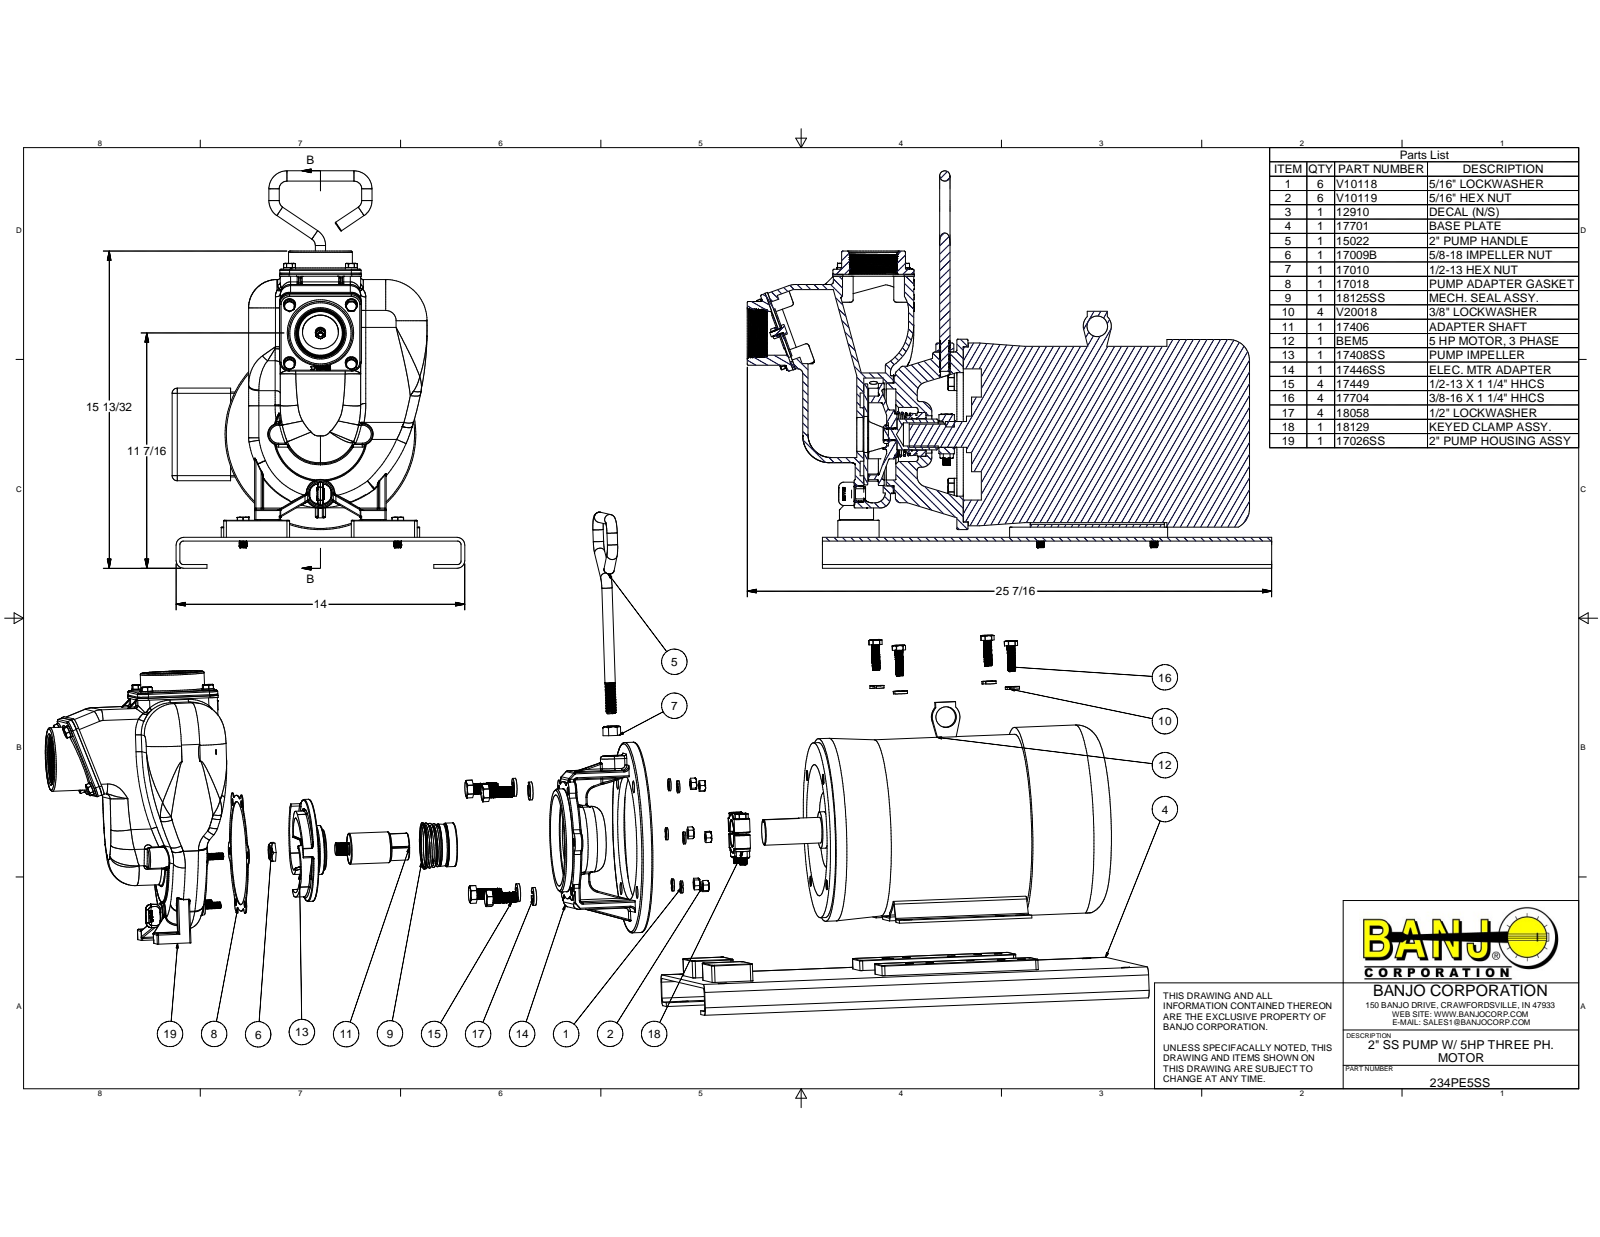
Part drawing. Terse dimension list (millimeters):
name: 17026SSX; 17000SS; 17002SS; 17014 (+8 more)
written by: Autodesk Inventor 2014 (AUTOMOTIVE_DESIGN)
unit: mm
bodies: 83 solids, 7004 faces (1211 planar, 2504 cylindrical, 3289 other)
size: 646.18 × 490.32 × 360.48
volume: 18 950 000 mm³; area: 1 909 000 mm²
holes: 17× ⌀6.4, 14× ⌀8.18, 12× ⌀7.8, 10× ⌀10.41, 8× ⌀9.13, 6× ⌀6.41, 6× ⌀7.94, 6× ⌀9.52, 6× ⌀9.78, 5× ⌀10.59, 4× ⌀13, 4× ⌀14.27
bosses: 132× ⌀6.82, 106× ⌀8.24, 60× ⌀11.07, 14× ⌀14.81, 12× ⌀5.39, 10× ⌀7.94, 9× ⌀12.7, 6× ⌀17.46
rounds: 84× R1.52, 74× R0.76, 66× R6.35, 57× R3.17, 29× R2.29, 24× R12.7, 17× R1.59, 16× R11.91
face distances: 4.55, 33.55, 12.7, 17.25, 38.1, 6.35, 29, 46.25, 50.8, 7.87
hole spacings: 76.2, 53.88, 71.44, 53.89, 107.76, 130.35, 107.77, 123.74
